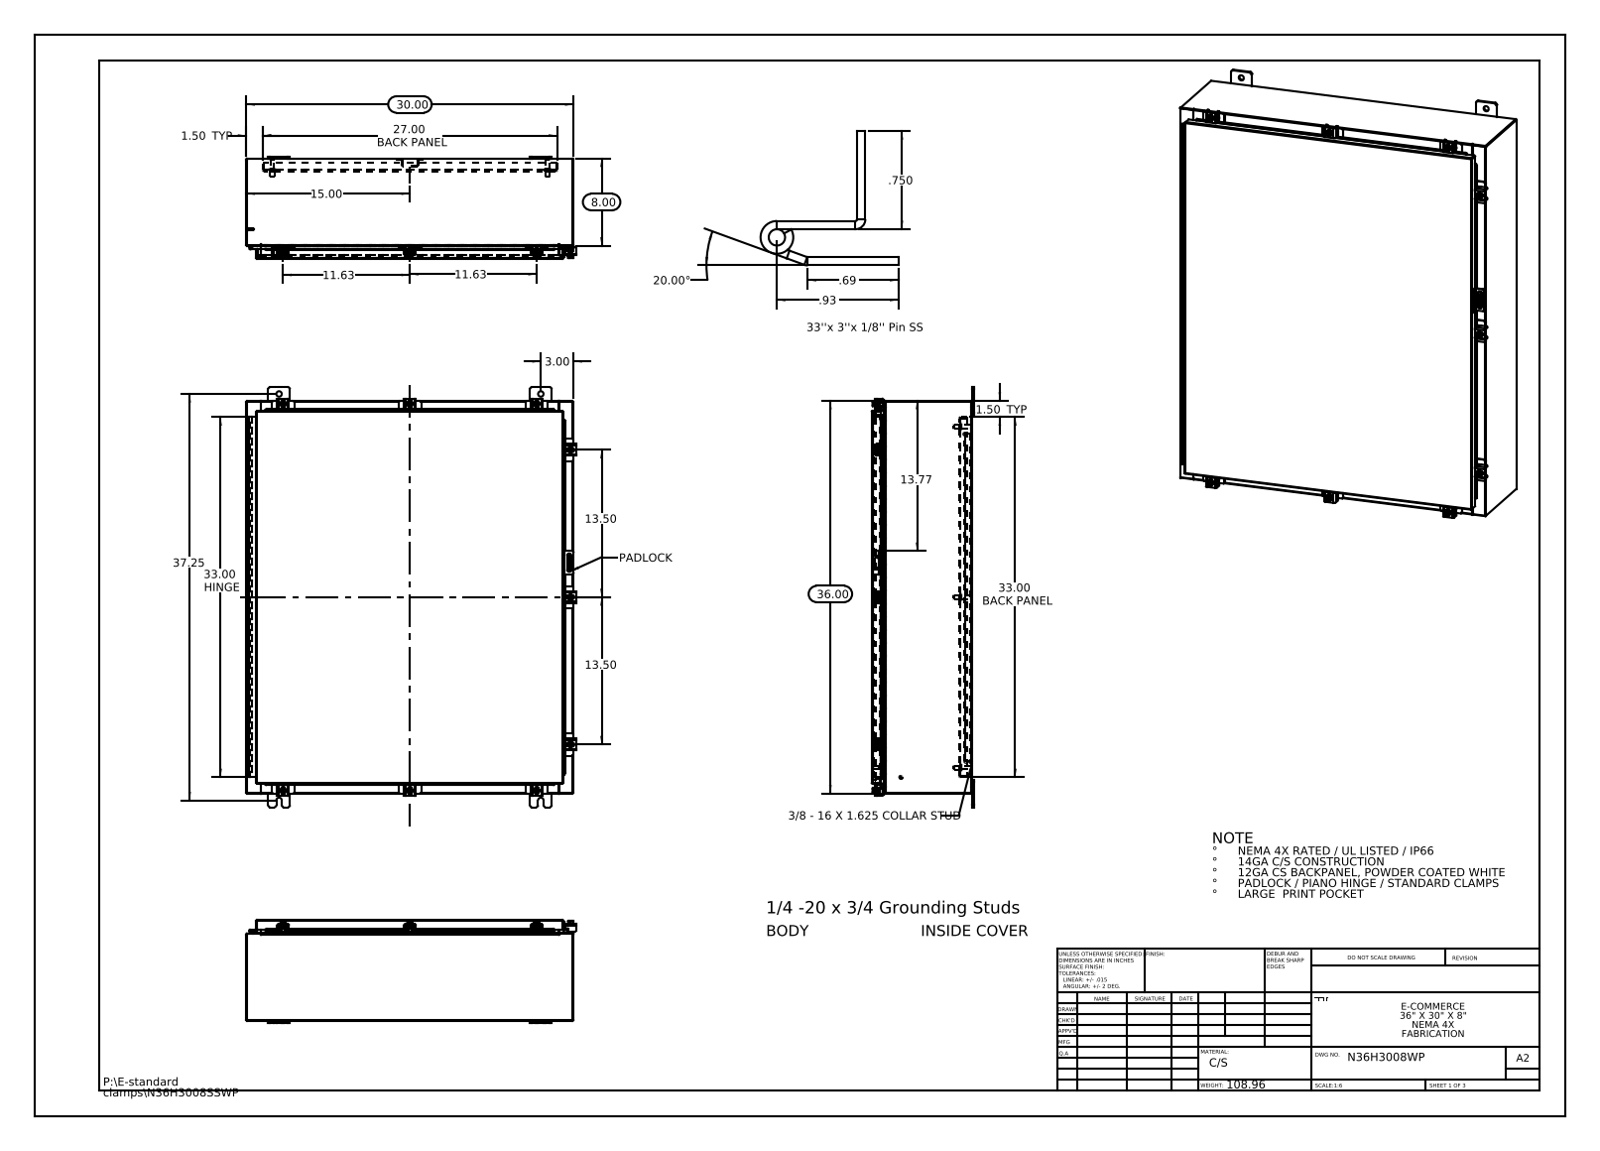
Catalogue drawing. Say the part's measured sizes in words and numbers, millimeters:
The part is named "N36H3008SSWP 22104005_DEFAULT; N36H3008SSWP Enclosure Stiffener; N36H3008SSWP Hinge Cover Side; N36H3008SSWP Backpanel (+8 more)". Its 3-D file was written by "SolidWorks 2013 (CONFIG_CONTROL_DESIGN)". It is 67 solids with 2482 faces: 1294 planar, 1036 cylindrical and 152 other. Overall it measures 977.9 by 767.4 by 238.5 millimeters. Its volume is 6 268 000 cubic millimeters and its surface area 6 142 000 square millimeters. Round holes: 10 of diameter 12.7, 9 of diameter 5.4, 9 of diameter 6.6, 2 of diameter 3.2. Round bosses or shafts: 10 of diameter 6.4, 9 of diameter 12.7, 9 of diameter 10.1, 6 of diameter 15.9, 6 of diameter 9.5, 6 of diameter 8.4, 2 of diameter 8, 2 of diameter 6. Partial cylindrical surfaces (rounded edges, fillets, slot ends): 42 of radius 1.5, 31 of radius 0.3, 25 of radius 2.2, 24 of radius 4.8, 18 of radius 3, 18 of radius 3.6, 13 of radius 1.3, 12 of radius 2. The main face-to-face distances are 1.9, 231.8, 229.9, 233.7, 2.6, 25.4, 206.4, 27.3, 204.5, 29.9. The hole center spacings are 396.9, 451, 754.2, 847.5, 947.6, 641.4, 900.5, 47.2.
